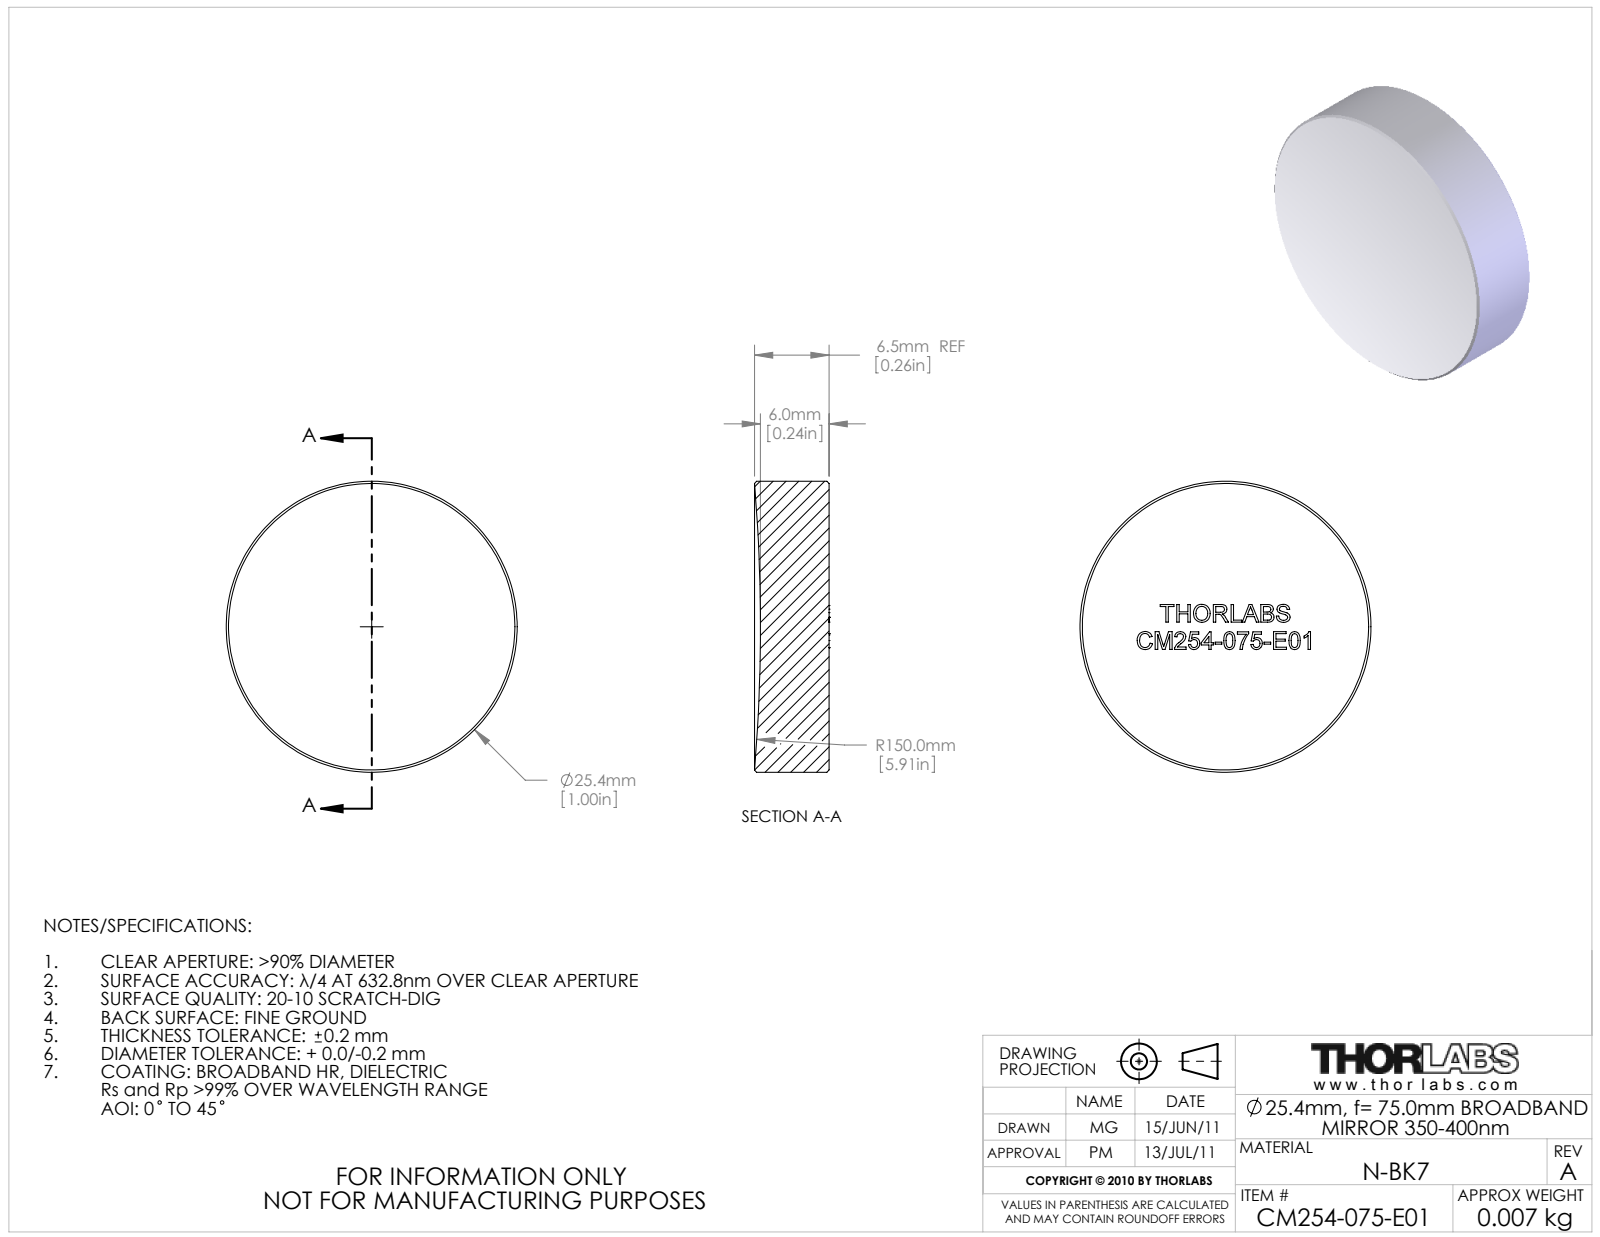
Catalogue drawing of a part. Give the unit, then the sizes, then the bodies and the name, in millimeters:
Units: millimetres
Overall size (bounding box): 25.4 × 25.4 × 6.52
Round bosses / shafts (diameter × count): ⌀25.4 ×1
Bodies: 0 solids, 39 faces (30 planar, 2 cylindrical, 7 other)
Part name (STEP PRODUCT): 22613-E0W
STEP written by: SolidWorks 2011 (AUTOMOTIVE_DESIGN)
